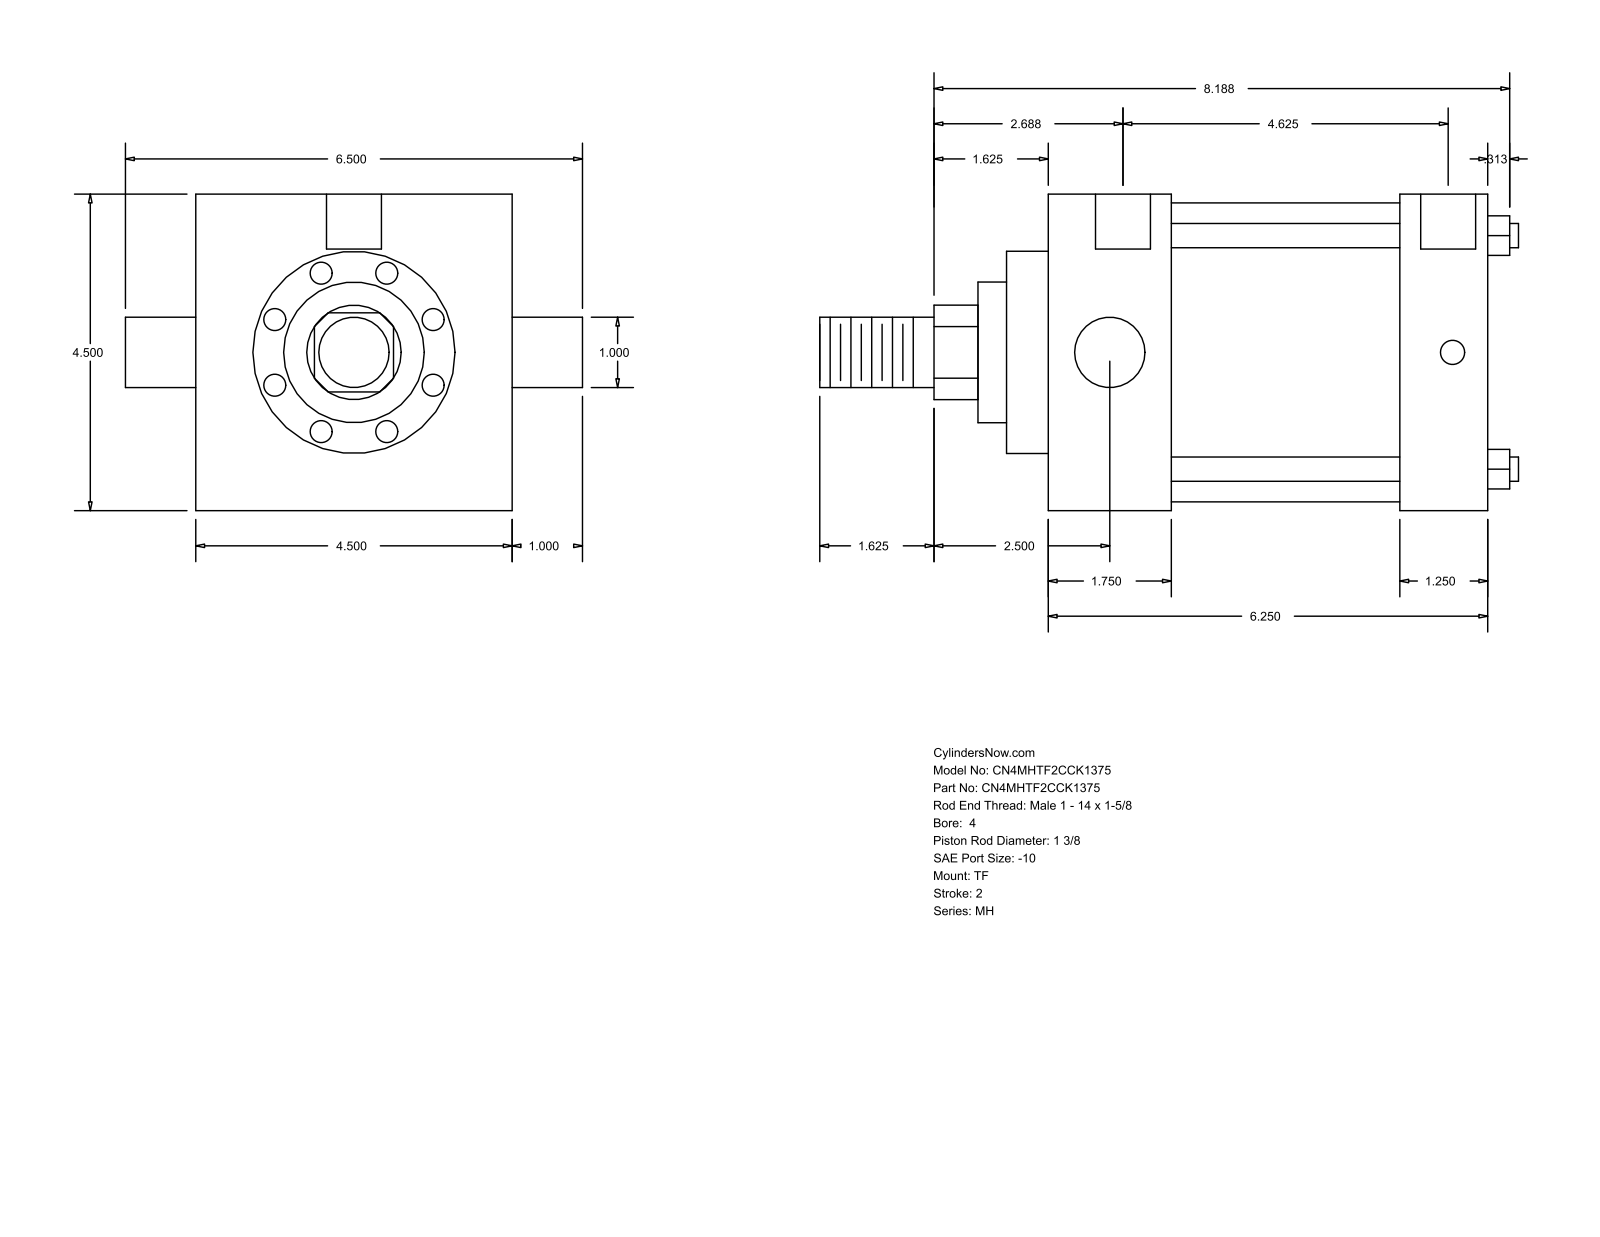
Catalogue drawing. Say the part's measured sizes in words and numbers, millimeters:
The part is named "MH_TF__0400_1.375". Its 3-D file was written by "GSSL Pune (CONFIG_CONTROL_DESIGN)". It is 0 solids with 86 faces: 61 planar, 25 cylindrical and 0 other. Overall it measures 252.41 by 165.1 by 114.3 millimeters. Round holes: 3 of diameter 8.73, 2 of diameter 19.84. Round bosses or shafts: 4 of diameter 8.76, 2 of diameter 25.4, 1 of diameter 107.95, 1 of diameter 73.03, 1 of diameter 50.8, 1 of diameter 34.92. Partial cylindrical surfaces (rounded edges, fillets, slot ends): 1 of radius 17.06. The main face-to-face distances are 114.3, 158.76, 44.45, 114.31, 127.01, 82.56, 31.75, 15.08, 59.53, 142.09. The hole center spacings are 1.58, 1.59, 117.48, 119.06, 119.07, 120.65.
